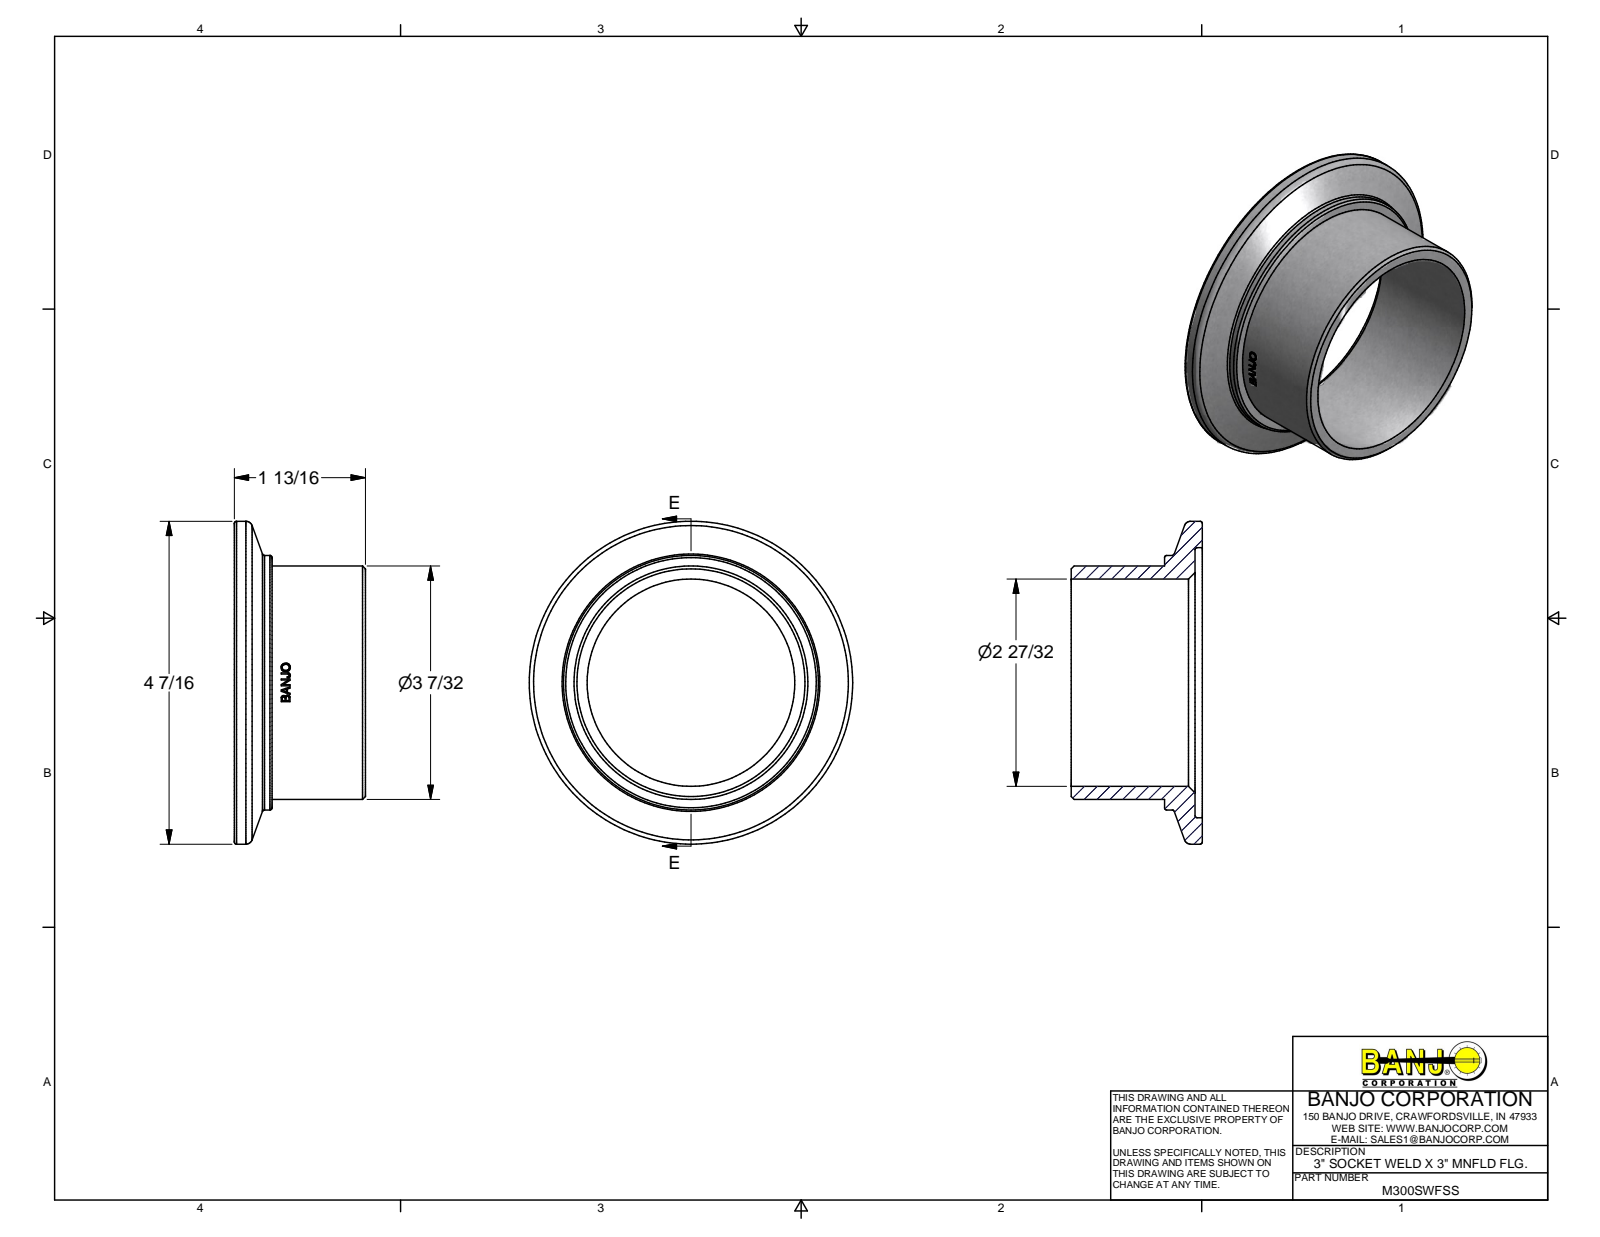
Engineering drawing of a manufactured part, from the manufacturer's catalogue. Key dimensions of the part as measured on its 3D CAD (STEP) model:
Part name (STEP PRODUCT): M300SWFSS
STEP written by: Autodesk Inventor 2014 (AUTOMOTIVE_DESIGN)
Units: millimetres
Bodies: 1 solid, 250 faces (96 planar, 25 cylindrical, 129 other)
Overall size (bounding box): 112.78 × 112.78 × 45.72
Volume: 84 481 mm³ · Surface area: 33 019 mm²
Round holes (diameter × count): ⌀72.39 ×1, ⌀94.31 ×1
Round bosses / shafts (diameter × count): ⌀112.78 ×1, ⌀88.9 ×1, ⌀81.53 ×1
Partial cylindrical surfaces — rounded edges, fillets, slot ends (radius × count): R40.01 ×1
Main face-to-face distances: 2.54, 43.18, 45.72, 32.56, 10.62, 13.16, 0.39, 3.05, 6.29, 5.57
